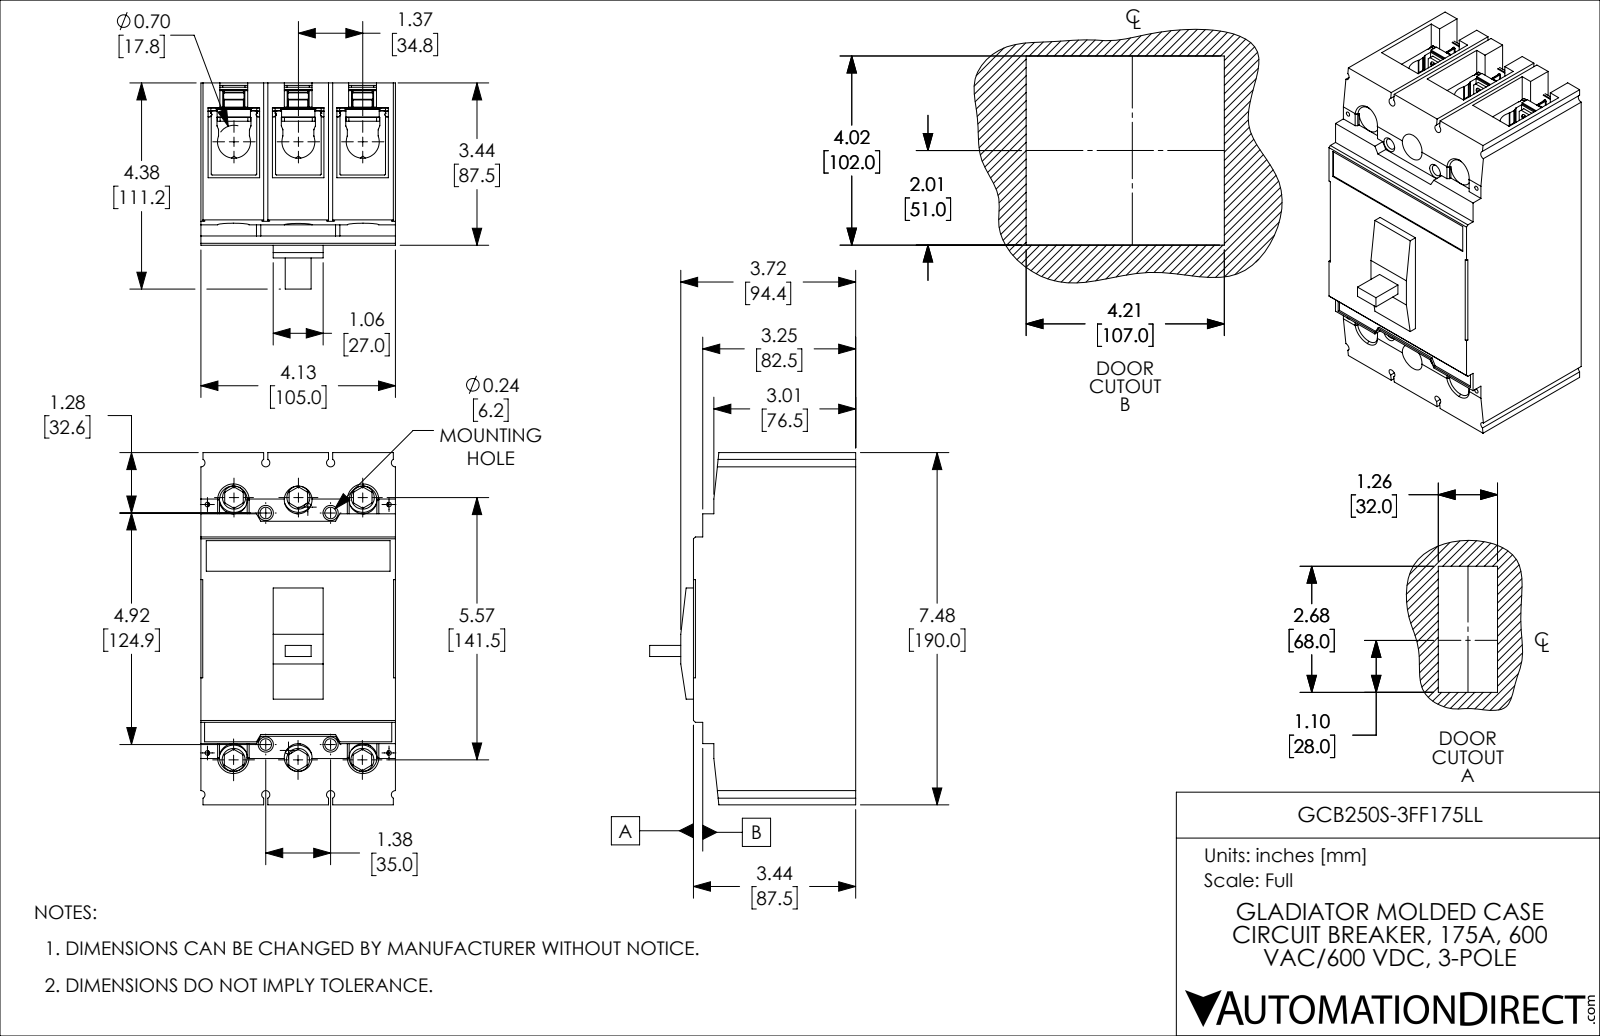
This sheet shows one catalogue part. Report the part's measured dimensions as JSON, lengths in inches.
{"part_name": "GCB250S-3FF175LL", "step_written_by": "SolidWorks 2021 (CONFIG_CONTROL_DESIGN)", "units": "inches", "bodies": {"solids": 25, "faces": 2233, "planar": 975, "cylindrical": 958, "other": 300}, "overall_size": [7.48, 4.378, 4.134], "volume_in3": 87.11, "surface_area_in2": 315.7, "round_holes": [[0.067, 24], [0.157, 24], [0.098, 10], [0.354, 6], [0.591, 6], [0.689, 6], [0.173, 4], [0.244, 4]], "round_bosses_or_shafts": [[0.709, 6]], "partial_cylinders_radius": [[0.012, 206], [0.039, 72], [0.059, 36], [0.02, 26], [0.008, 24], [0.079, 20], [0.016, 12], [0.031, 12]], "face_to_face_distances": [1.368, 4.134, 2.736, 1.094, 0.843, 0.252, 0.059, 1.378, 6.102, 3.445], "hole_center_spacings": [0.285, 0.743, 1.046, 1.378, 5.24, 6.298, 1.368, 1.426]}
